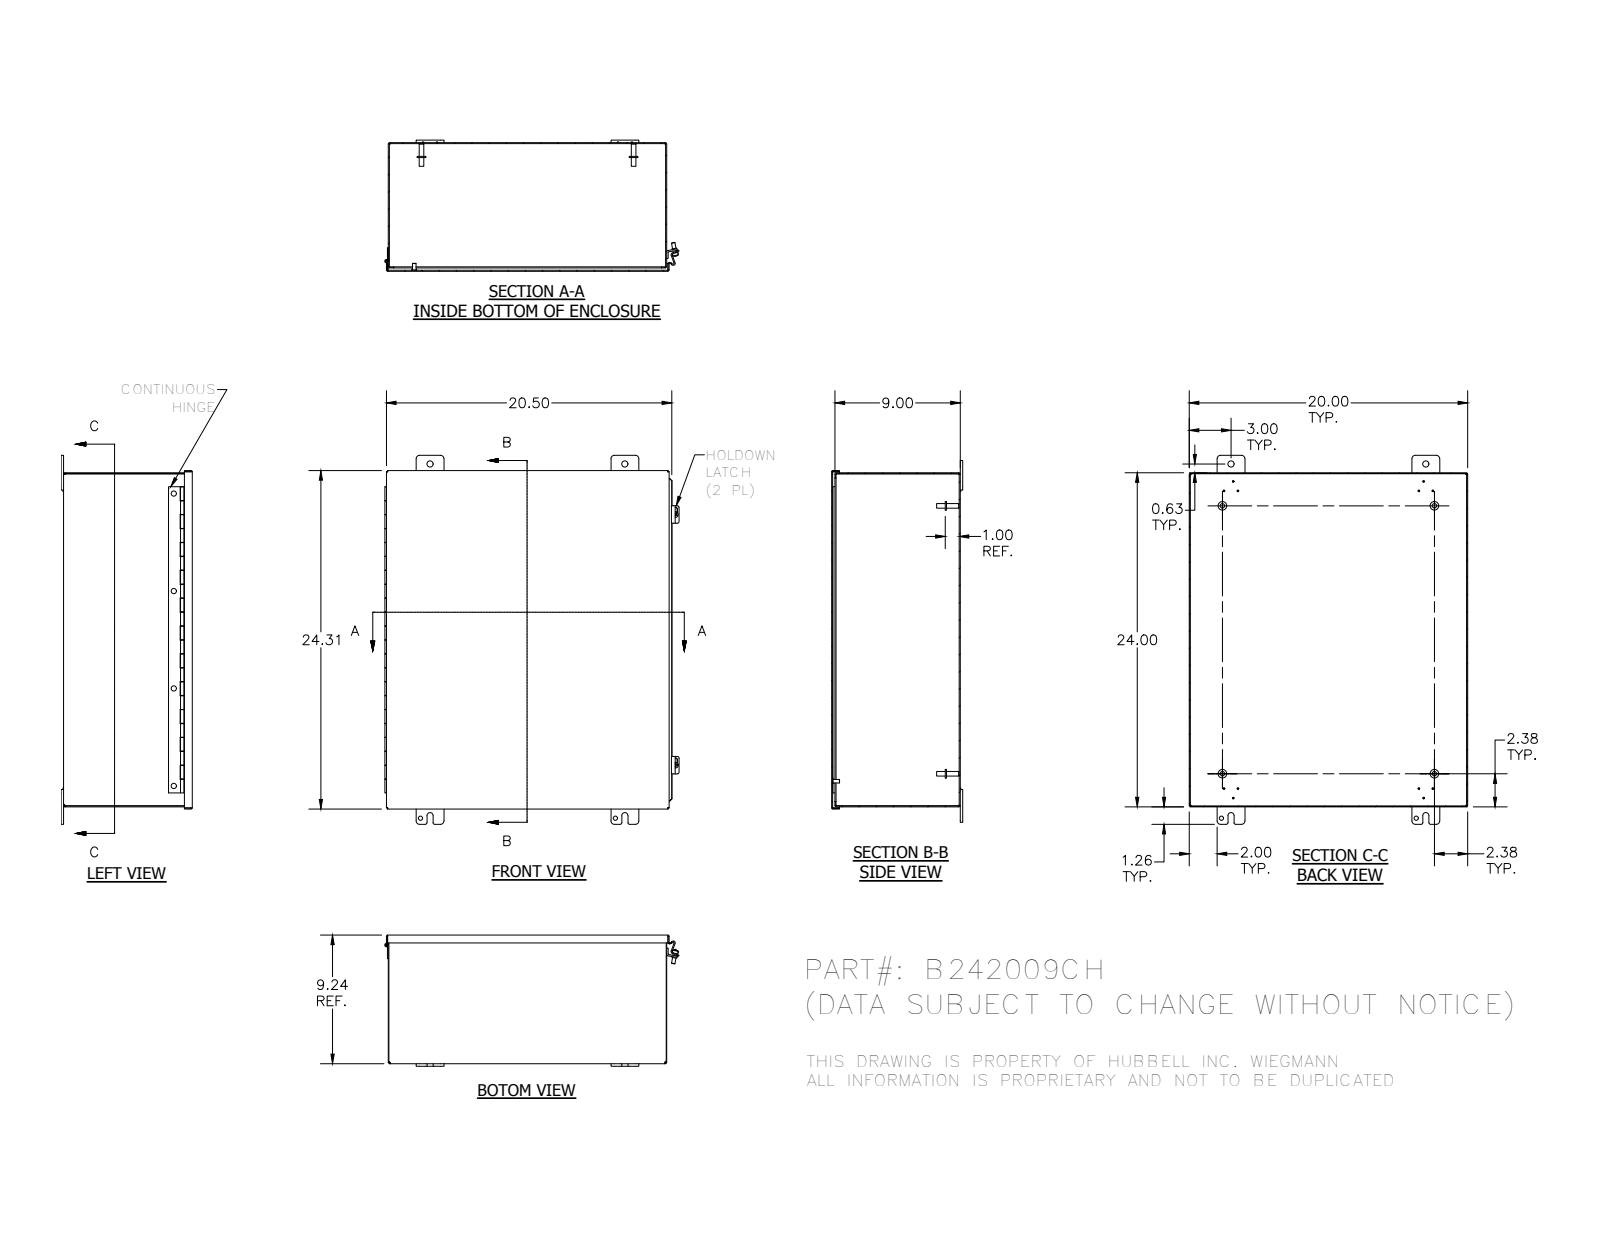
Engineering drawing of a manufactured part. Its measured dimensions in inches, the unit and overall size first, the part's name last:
Units: inches
Overall size (bounding box): 26.505 × 21.136 × 9.423
Round holes (diameter × count): ⌀0.11 ×4, ⌀0.313 ×4, ⌀0.375 ×4, ⌀0.438 ×4, ⌀0.196 ×2, ⌀0.125 ×1, ⌀0.125 ×1
Round bosses / shafts (diameter × count): ⌀0.625 ×4, ⌀0.33 ×4, ⌀0.25 ×4, ⌀0.41 ×2, ⌀0.344 ×2, ⌀0.337 ×1, ⌀0.12 ×1
Partial cylindrical surfaces — rounded edges, fillets, slot ends (radius × count): R0.125 ×16, R0.25 ×16, R0.031 ×8, R0.063 ×8, R0.07 ×8, R0.105 ×8, R0.016 ×5, R0.09 ×5
Main face-to-face distances: 0.074, 9.169, 9.243, 9.095, 19.926, 23.926, 20, 19.852, 24, 23.852
Hole centre spacings: 14, 1.593, 7, 18, 24.005, 27.789, 0.75, 13.39
Volume: 142.2 in³ · Surface area: 3 836 in²
Bodies: 20 solids, 649 faces (395 planar, 185 cylindrical, 69 other)
Part name (STEP PRODUCT): B242009CH; B242009CHBKP; B2420CHLID; H6010101 (+8 more)
STEP written by: Autodesk Inventor 2012 (AUTOMOTIVE_DESIGN)
